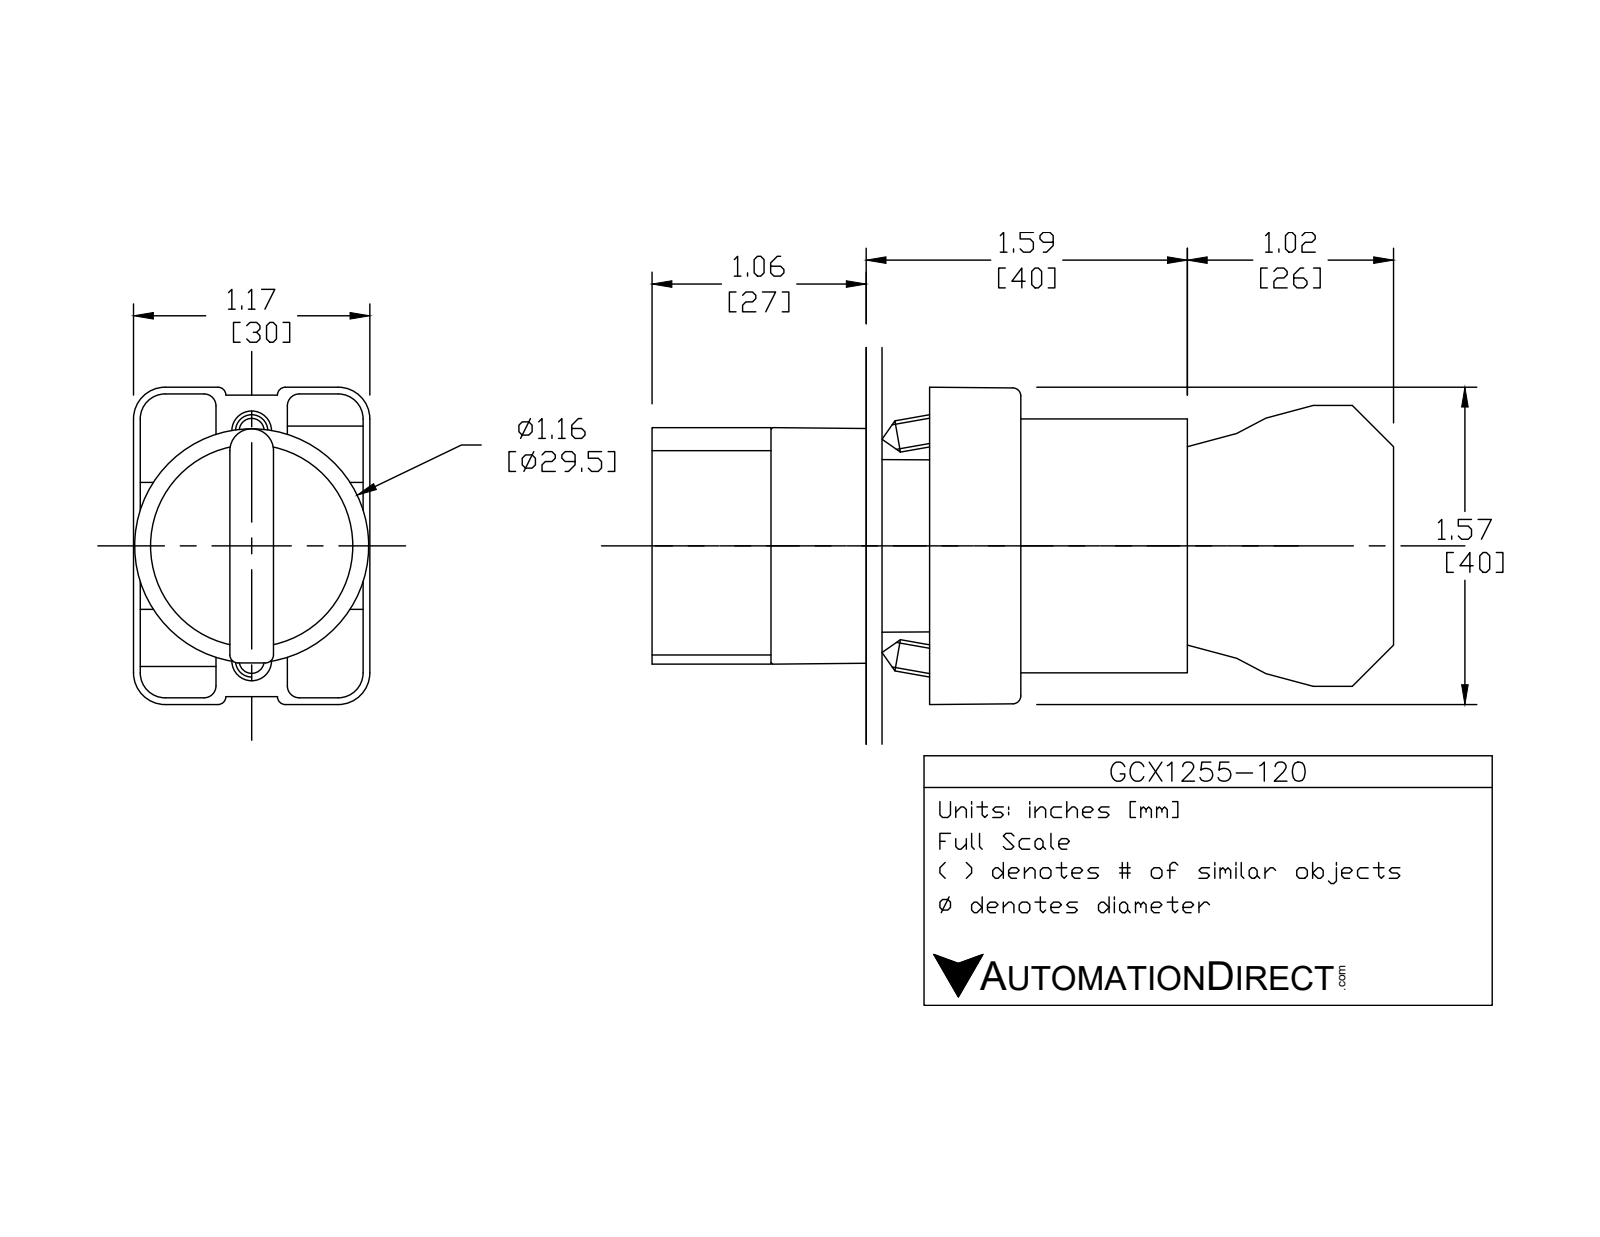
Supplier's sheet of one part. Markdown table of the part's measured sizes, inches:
| quantity | value |
| --- | --- |
| part name | GCX1255 OPERATOR; ECX1050; ecx1040; ecx1029 (+1 more) |
| STEP written by | SolidWorks 2016 (AUTOMOTIVE_DESIGN) |
| units | inches |
| bodies | 8 solids, 445 faces (263 planar, 151 cylindrical, 31 other) |
| overall size | 3.653 × 1.581 × 1.177 |
| volume | 2.799 in³ |
| surface area | 39 in² |
| round holes (diameter × count) | 0.079 × 2, 0.124 × 2, 0.13 × 2, 0.087 × 1, 0.197 × 1, 0.469 × 1, 0.878 × 1, 0.888 × 1, 1.024 × 1 |
| round bosses / shafts (diameter × count) | 0.157 × 4, 1.175 × 1, 1.004 × 1, 0.945 × 1, 0.856 × 1, 0.78 × 1, 0.504 × 1 |
| partial cylindrical surfaces (radius × count) | 0.059 × 24, 0.041 × 12, 0.124 × 12, 0.157 × 12, 0.039 × 9, 0.128 × 2, 0.02 × 1, 0.063 × 1 |
| main face-to-face distances | 0.827, 2.02, 1.193, 0.579, 1.244, 1.171, 0.472, 0.469, 0.031, 0.033 |
| hole center spacings | 0.236, 0.544, 0.472, 0.49 |
